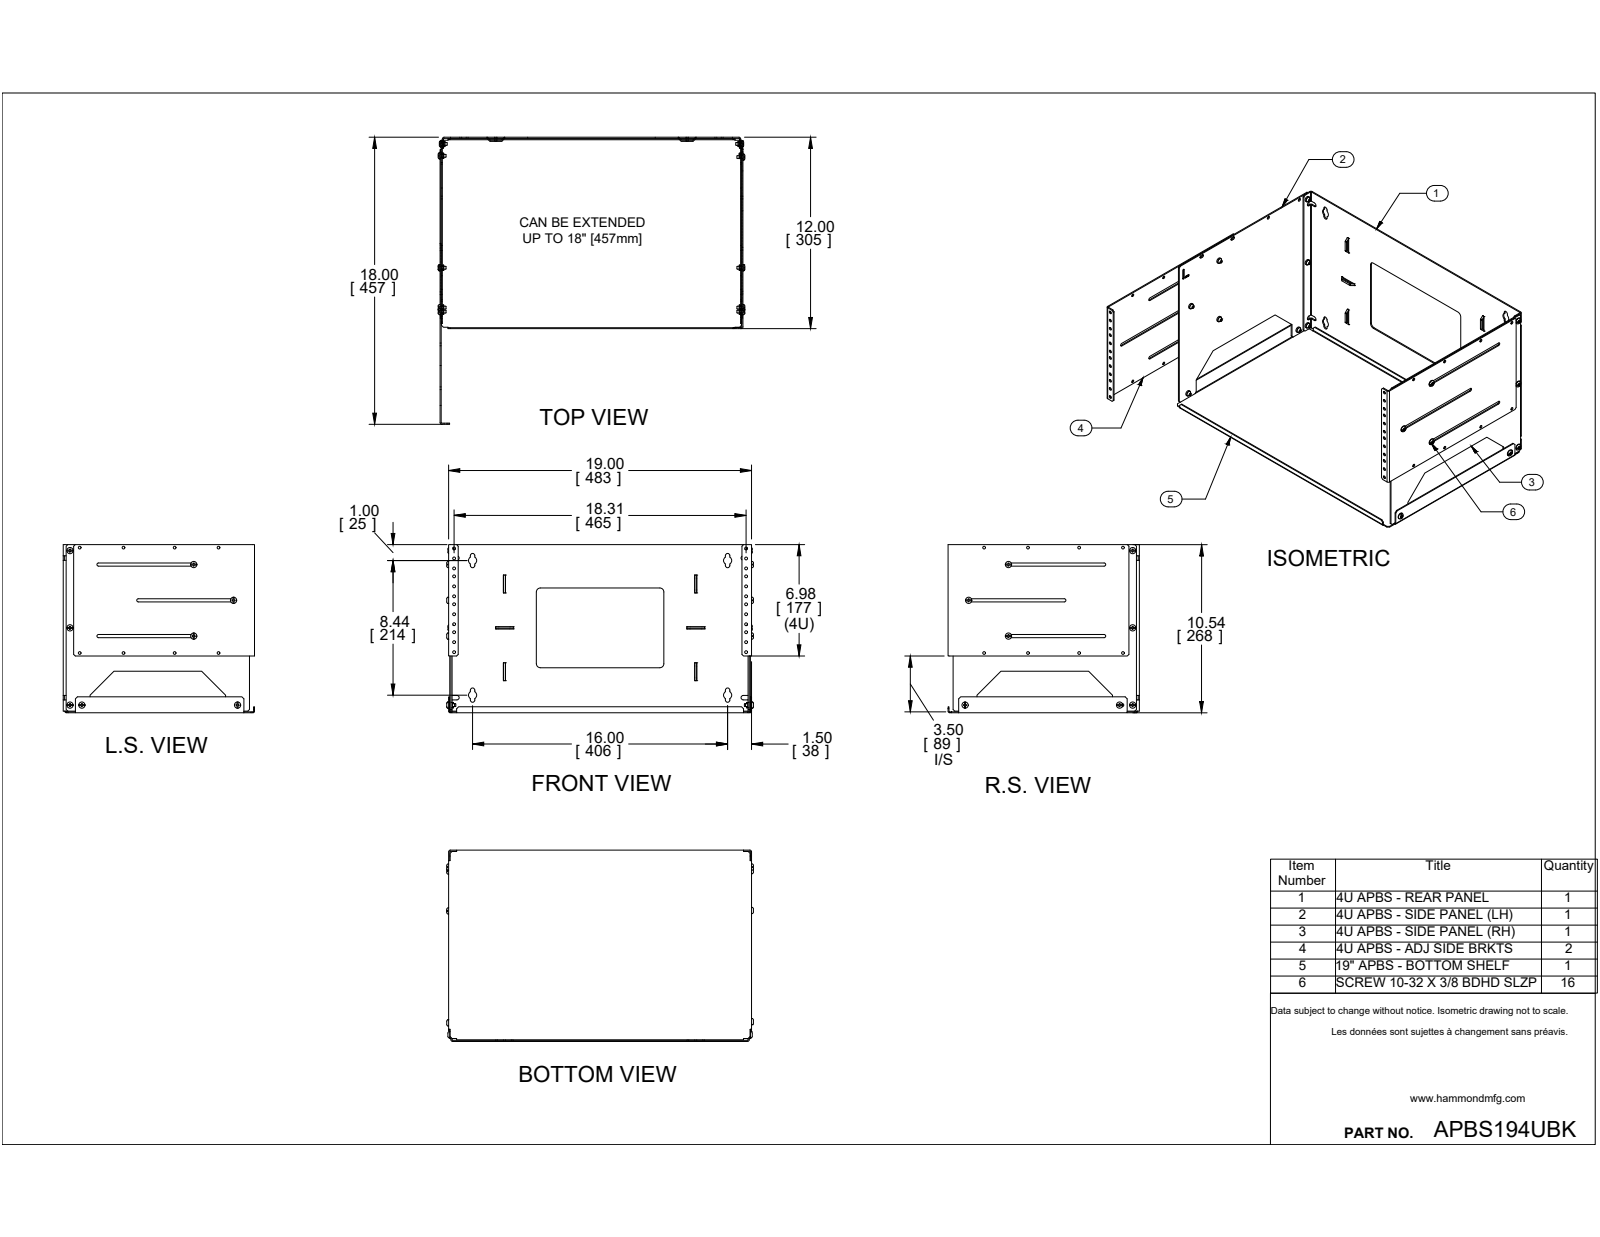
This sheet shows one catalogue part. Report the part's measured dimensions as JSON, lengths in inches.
{"part_name": "APBS194UBK", "step_written_by": "SolidWorks 2019 (CONFIG_CONTROL_DESIGN)", "units": "inches", "bodies": {"solids": 38, "faces": 876, "planar": 552, "cylindrical": 260, "other": 64}, "overall_size": [19.235, 12, 10.542], "volume_in3": 52.67, "surface_area_in2": 1607, "round_holes": [[0.177, 26], [0.159, 8], [0.17, 8], [0.25, 8], [0.201, 3]], "round_bosses_or_shafts": [[0.39, 12], [0.18, 12], [0.34, 8], [0.244, 8]], "partial_cylinders_radius": [[0.072, 16], [0.141, 14], [0.063, 7], [0.1, 6], [0.029, 4], [0.036, 4], [0.086, 4], [0.094, 4]], "face_to_face_distances": [0.072, 18.856, 18.784, 0.057, 0.144, 18.928, 18.712, 19, 0.057, 0.087], "hole_center_spacings": [1.75, 18.398, 18.325, 3.5, 18.314, 18.349, 0.625, 0.625]}
